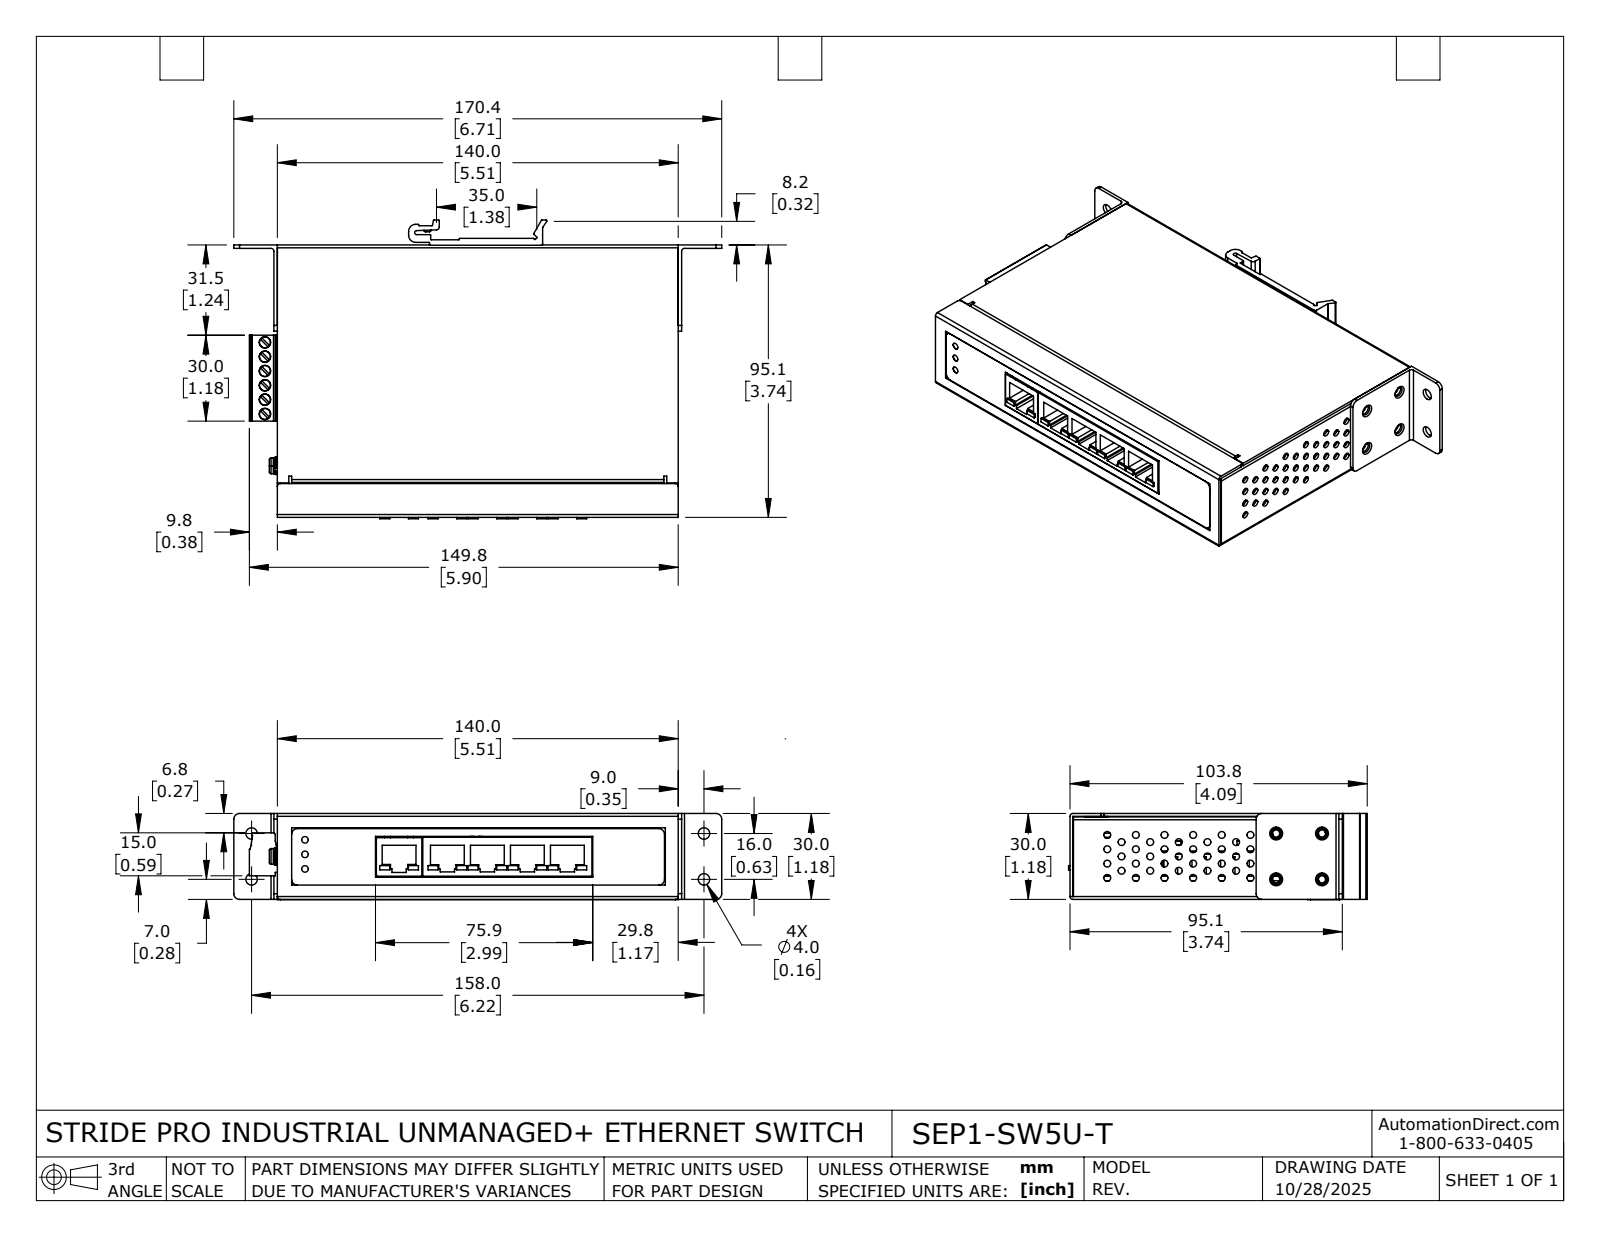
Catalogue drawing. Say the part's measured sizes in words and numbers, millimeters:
The part is named "SEP1-SW5U-T". Its 3-D file was written by "SolidWorks 2024 (AUTOMOTIVE_DESIGN)". It is 16 solids with 1912 faces: 1011 planar, 698 cylindrical and 203 other. Overall it measures 149.8 by 104.3 by 30.1 millimeters. Its volume is 86 620 cubic millimeters and its surface area 129 400 square millimeters. Round holes: 51 of diameter 2.4, 11 of diameter 2.5, 9 of diameter 4, 6 of diameter 1.4, 5 of diameter 2.8, 4 of diameter 3.2, 3 of diameter 2, 3 of diameter 2.3, 3 of diameter 3, 2 of diameter 3.5, 1 of diameter 1.5. Round bosses or shafts: 7 of diameter 4.1, 6 of diameter 3.8, 6 of diameter 0.5, 5 of diameter 5, 5 of diameter 3, 4 of diameter 5.4, 3 of diameter 4, 1 of diameter 5.5. Partial cylindrical surfaces (rounded edges, fillets, slot ends): 79 of radius 0.1, 29 of radius 0.2, 27 of radius 1, 20 of radius 0.3, 13 of radius 0.5, 11 of radius 2, 10 of radius 0.2, 6 of radius 0.9. The main face-to-face distances are 1, 29, 0.5, 28, 20.9, 21.9, 1.6, 22.5, 23.5, 7.1. The hole center spacings are 10, 11.2, 5, 20.6, 14.1, 20, 30.4, 22.4.
